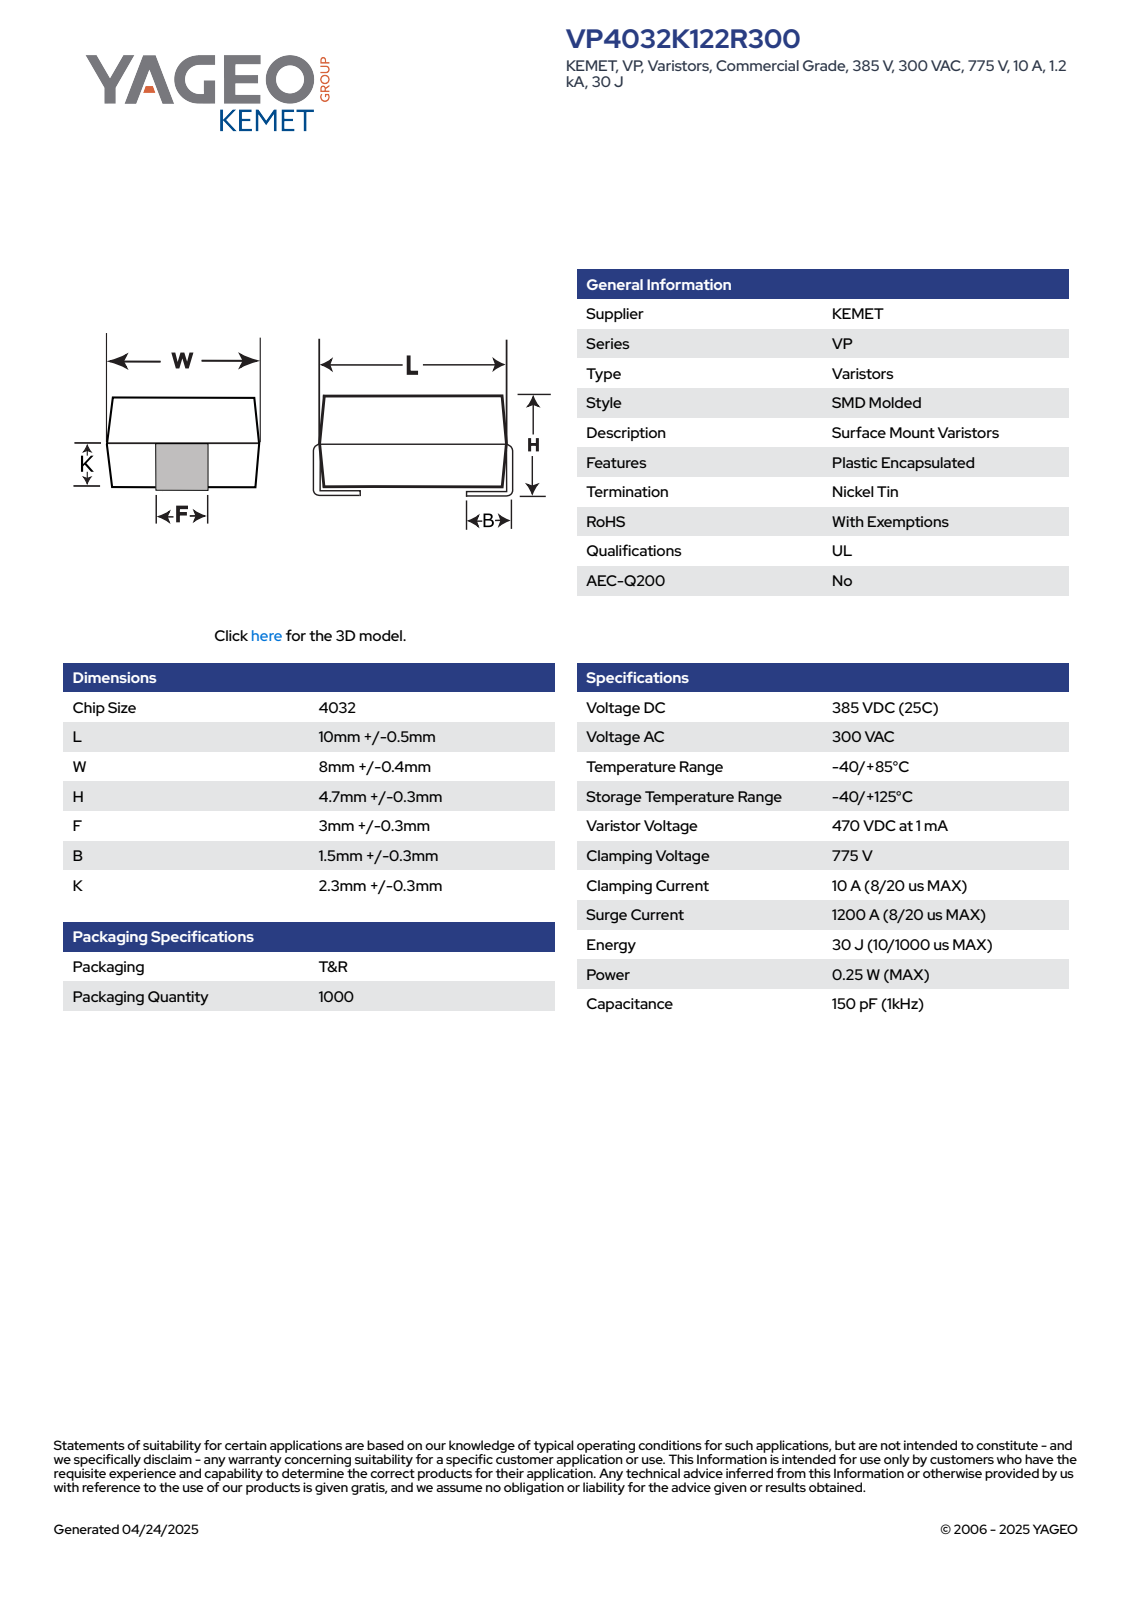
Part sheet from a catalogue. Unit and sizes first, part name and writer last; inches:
Units: inches
Overall size (bounding box): 0.438 × 0.331 × 0.197
Partial cylindrical surfaces — rounded edges, fillets, slot ends (radius × count): R0.01 ×4
Main face-to-face distances: 0.185, 0.408, 0.426, 0.197, 0.414, 0.438, 0.13, 0.071, 0.367, 0.059
Volume: 0.024 in³ · Surface area: 0.595 in²
Bodies: 4 solids, 87 faces (83 planar, 4 cylindrical, 0 other)
Part name (STEP PRODUCT): VS_MOLDED_4032_L10.5W8.4H5.00F3.3B1.8K2.60
STEP written by: SolidWorks 2014 (AUTOMOTIVE_DESIGN)
